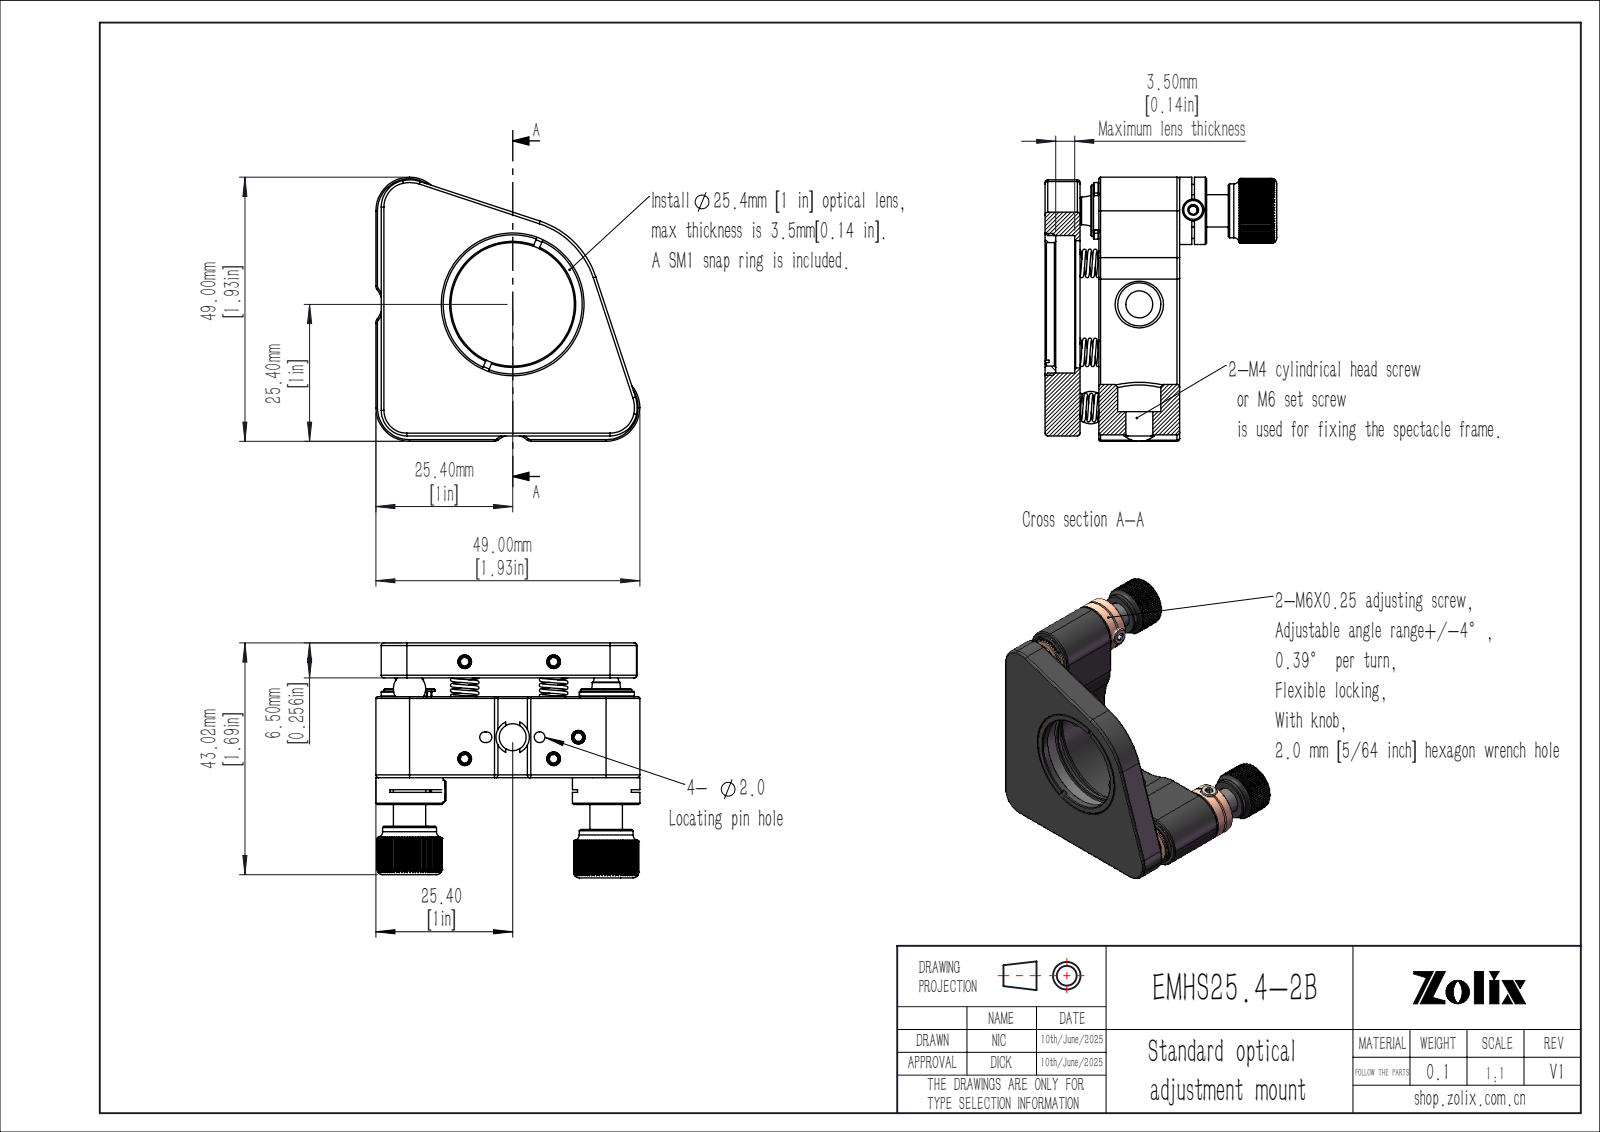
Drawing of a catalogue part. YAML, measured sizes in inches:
part_name: "EMHS25.4-2B"
step_written_by: "SolidWorks 2020 (CONFIG_CONTROL_DESIGN)"
units: inches
bodies: {solids: 0, faces: 998, planar: 458, cylindrical: 298, other: 242}
overall_size: [1.929, 1.929, 1.717]
round_holes:
  - {diameter: 0.236, count: 5}
  - {diameter: 0.118, count: 4}
  - {diameter: 0.079, count: 2}
  - {diameter: 0.197, count: 2}
  - {diameter: 0.315, count: 2}
  - {diameter: 0.157, count: 1}
  - {diameter: 0.181, count: 1}
  - {diameter: 0.248, count: 1}
  - {diameter: 0.394, count: 1}
  - {diameter: 0.902, count: 1}
  - {diameter: 0.929, count: 1}
  - {diameter: 1.004, count: 1}
round_bosses_or_shafts:
  - {diameter: 0.118, count: 4}
  - {diameter: 0.157, count: 3}
  - {diameter: 0.492, count: 2}
  - {diameter: 0.374, count: 2}
  - {diameter: 0.059, count: 2}
  - {diameter: 0.394, count: 1}
  - {diameter: 0.315, count: 1}
  - {diameter: 0.236, count: 1}
partial_cylinders:
  - {radius: 0.02, count: 12}
  - {radius: 0.039, count: 8}
  - {radius: 0.012, count: 4}
  - {radius: 0.031, count: 4}
  - {radius: 0.246, count: 3}
  - {radius: 0.122, count: 2}
  - {radius: 0.171, count: 2}
  - {radius: 0.197, count: 2}
face_to_face_distances: [0.256, 0.984, 0.728, 0.039, 0.138, 0.089, 0.108, 0.177, 0.453, 0.492]
hole_center_spacings: [0.65, 0.188, 0.197, 0.338, 0.384, 0.384, 0.569, 0.811]
